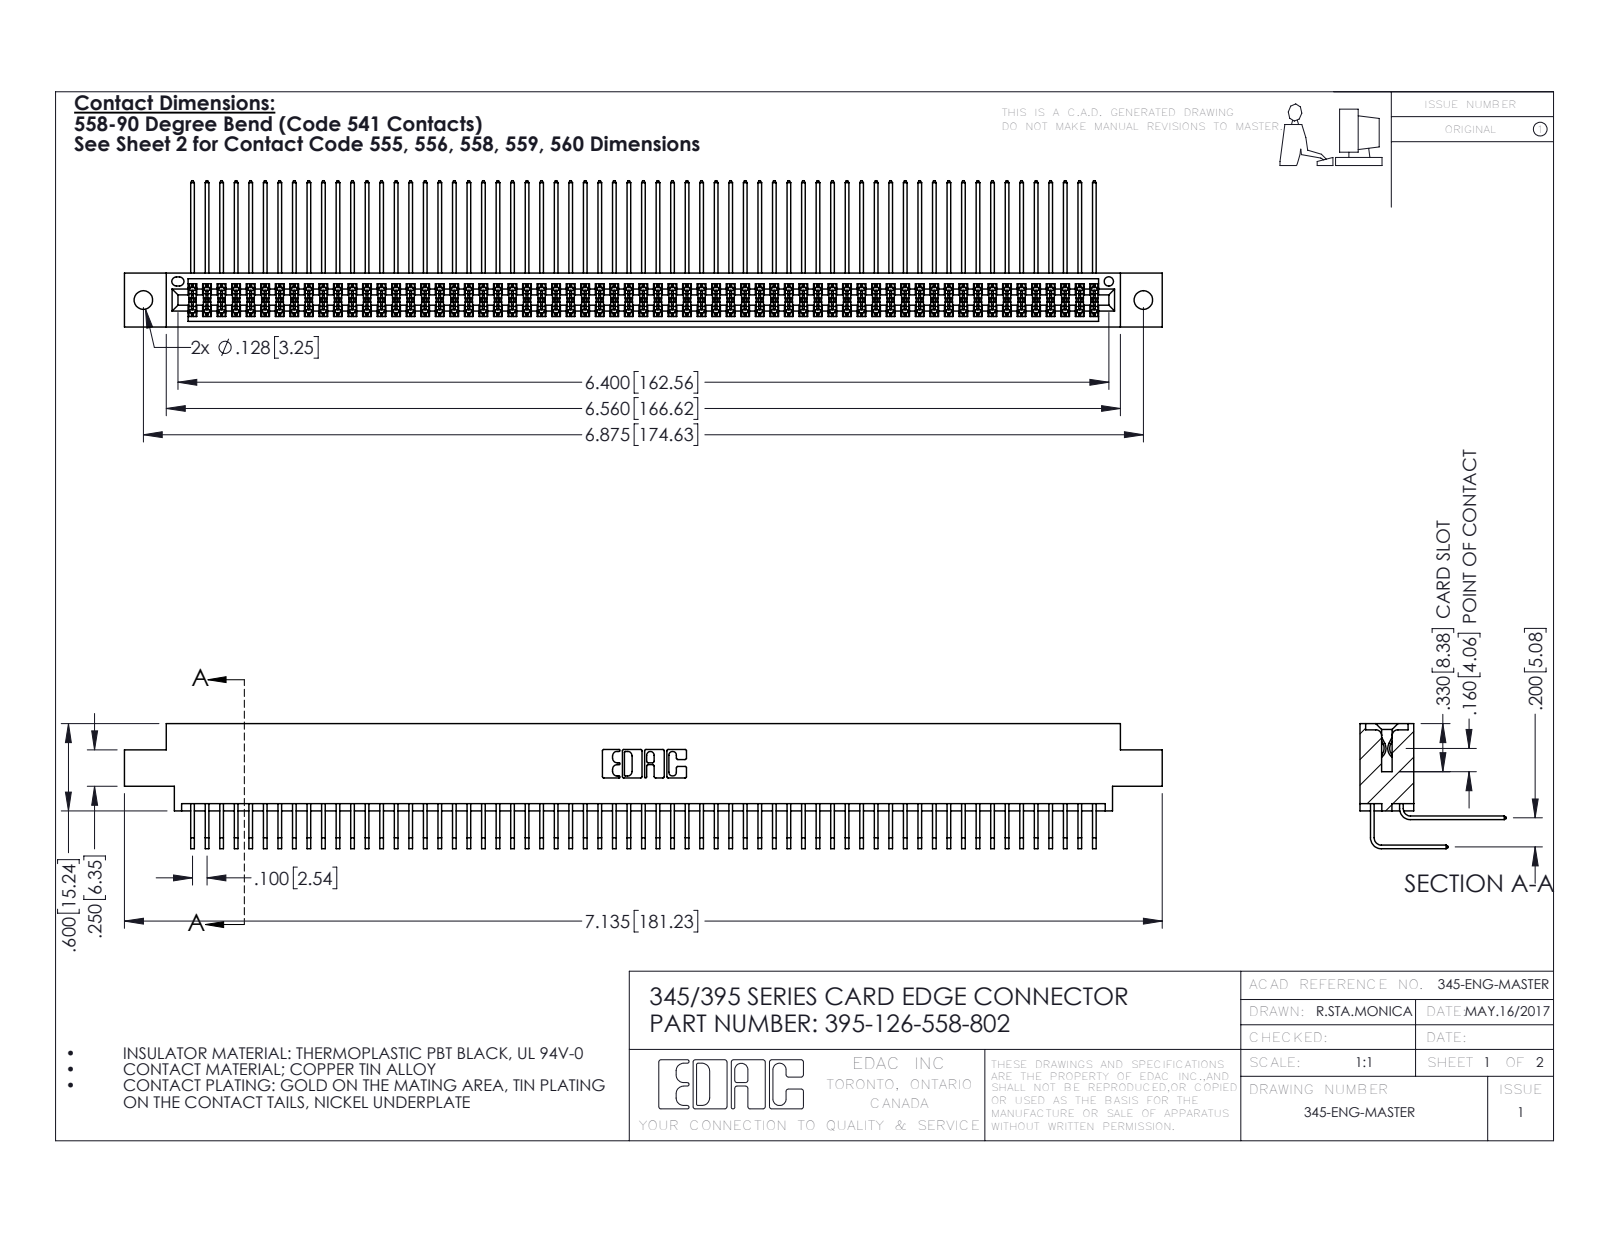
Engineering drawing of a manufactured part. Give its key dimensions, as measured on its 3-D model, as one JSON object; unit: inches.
{"part_name": "345-292-001_558 559 Tail - 1; 345 Part_0.170 Offset - 0.128 Dia; 395-126-558-802; 345-292-001_558 Tail - 2", "step_written_by": "SolidWorks 2016 (CONFIG_CONTROL_DESIGN)", "units": "inches", "bodies": {"solids": 127, "faces": 6682, "planar": 4494, "cylindrical": 2188, "other": 0}, "overall_size": [7.135, 1.005, 0.859], "volume_in3": 1.121, "surface_area_in2": 47.83, "round_holes": [[0.128, 2], [0.064, 1]], "partial_cylinders_radius": [[0.006, 190], [0.01, 22], [0.007, 6], [0.031, 6], [0.026, 3], [0.014, 2], [0.019, 2], [0.022, 2]], "face_to_face_distances": [0.072, 0.298, 0.2, 0.37, 0.098, 0.272, 0.025, 0.225, 0.175, 0.025], "hole_center_spacings": [0.27, 6.639, 6.875]}
